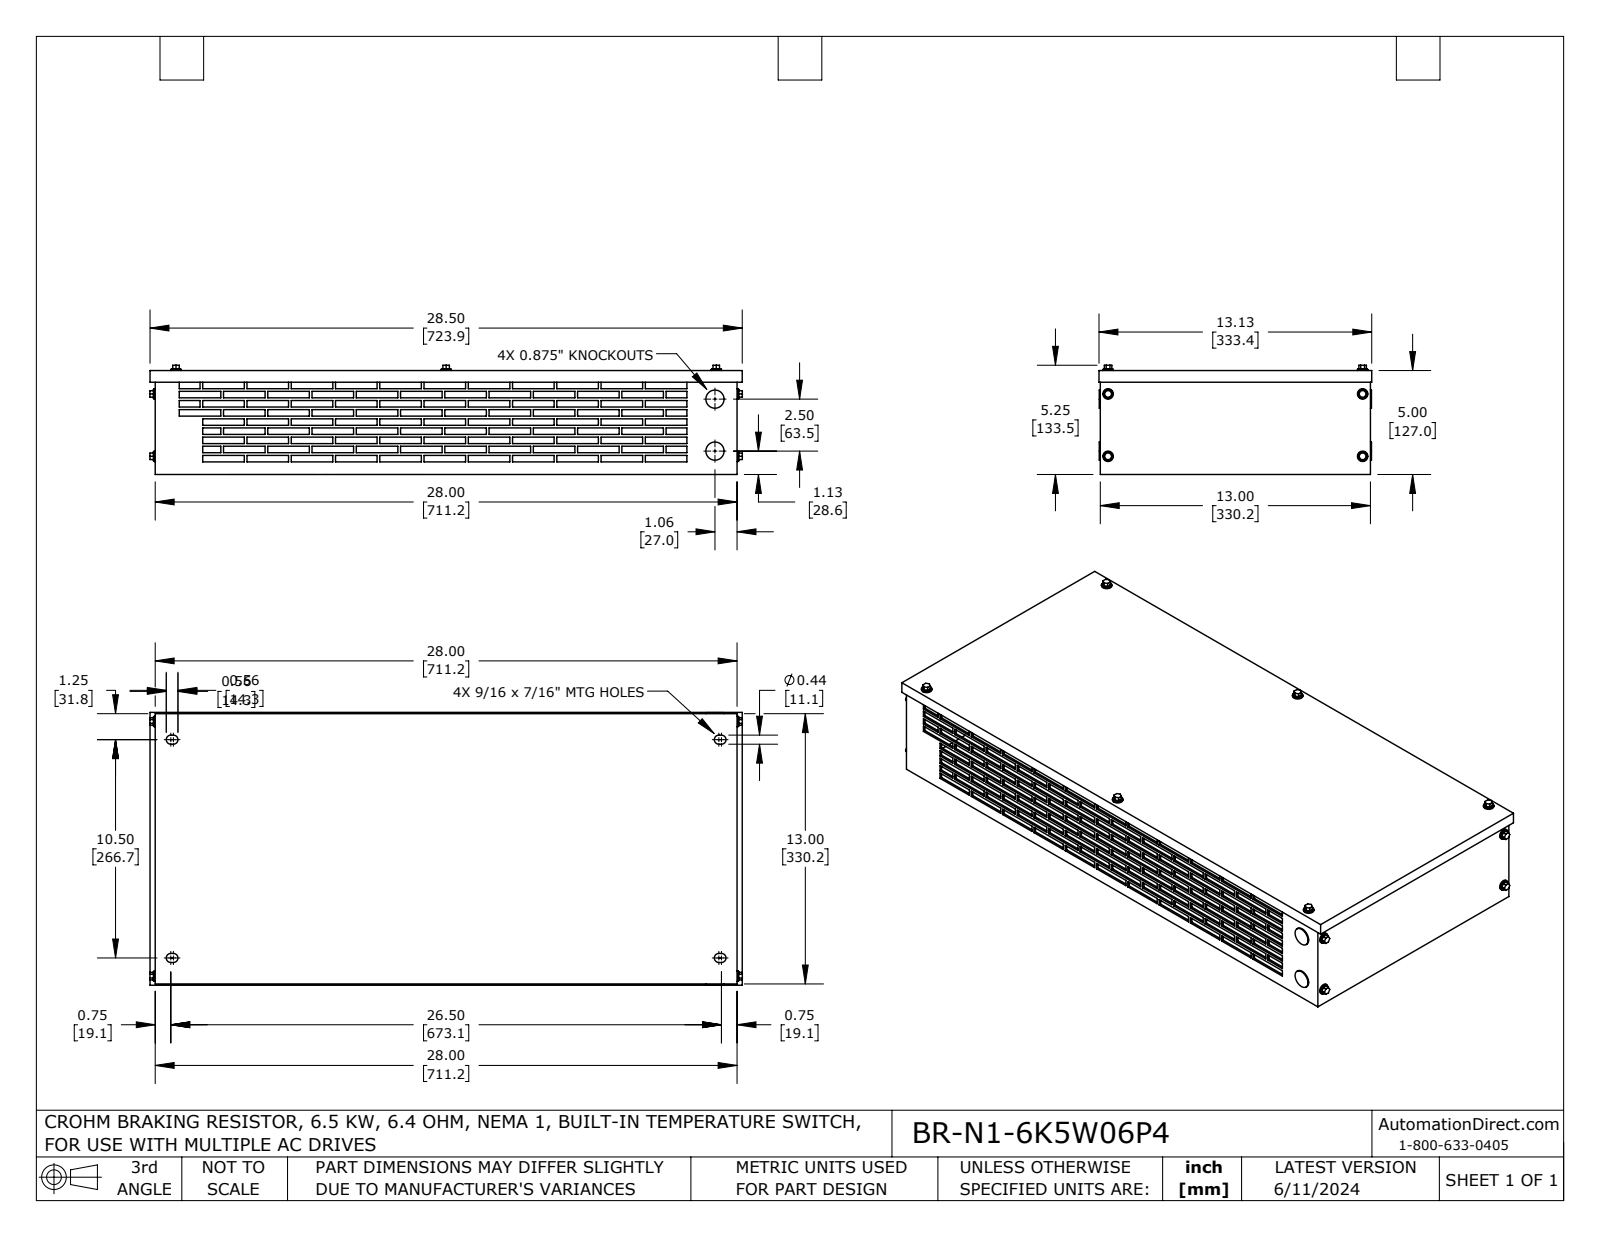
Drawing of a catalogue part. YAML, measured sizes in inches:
part_name: "BR-N1-6K5W06P4"
step_written_by: "SolidWorks 2021 (AUTOMOTIVE_DESIGN)"
units: inches
bodies: {solids: 33, faces: 1120, planar: 1012, cylindrical: 108, other: 0}
overall_size: [28.509, 13.125, 5.254]
volume: 101.7
surface_area: 2139
round_holes:
  - {diameter: 0.25, count: 10}
  - {diameter: 0.75, count: 2}
round_bosses_or_shafts:
  - {diameter: 0.5, count: 10}
  - {diameter: 0.437, count: 10}
  - {diameter: 0.875, count: 2}
partial_cylinders:
  - {radius: 0.219, count: 8}
face_to_face_distances: [0.1, 4.9, 5, 4.8, 12.9, 27.9, 13, 12.8, 28, 27.8]
hole_center_spacings: [12.25, 13, 17.862, 3, 12.611, 26, 28.741, 2.5]
